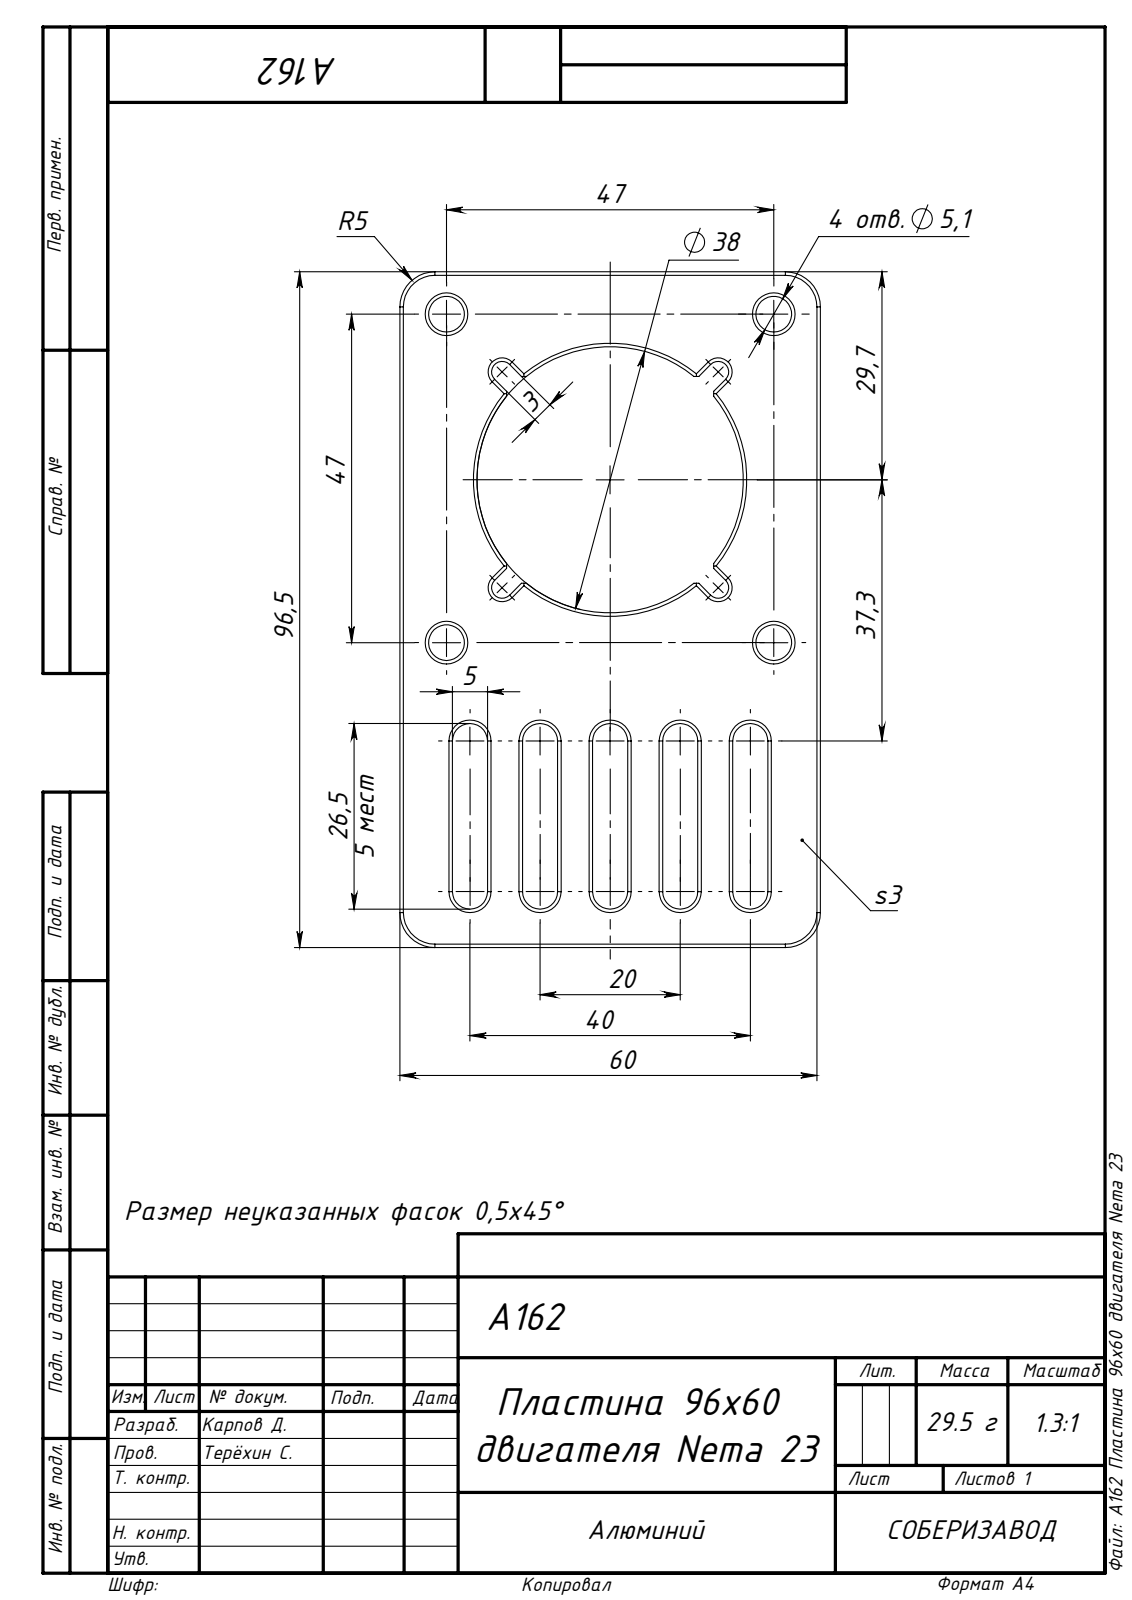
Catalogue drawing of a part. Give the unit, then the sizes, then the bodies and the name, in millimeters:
Units: millimetres
Overall size (bounding box): 96.5 × 60 × 3
Round holes (diameter × count): ⌀5.1 ×4, ⌀38 ×1
Partial cylindrical surfaces — rounded edges, fillets, slot ends (radius × count): R2.5 ×10, R1.5 ×4, R5 ×4
Main face-to-face distances: 3, 5, 10, 15, 20, 25, 60, 30, 35, 96.5
Hole centre spacings: 32.95, 33.23, 46.7, 46.9, 66.19
Volume: 11 502 mm³ · Surface area: 9 930 mm²
Bodies: 1 solid, 130 faces (54 planar, 38 cylindrical, 38 other)
Part name (STEP PRODUCT): A162 Пластина 96x60 двигателя Nema 23
STEP written by: SolidWorks 2018 (AUTOMOTIVE_DESIGN)
